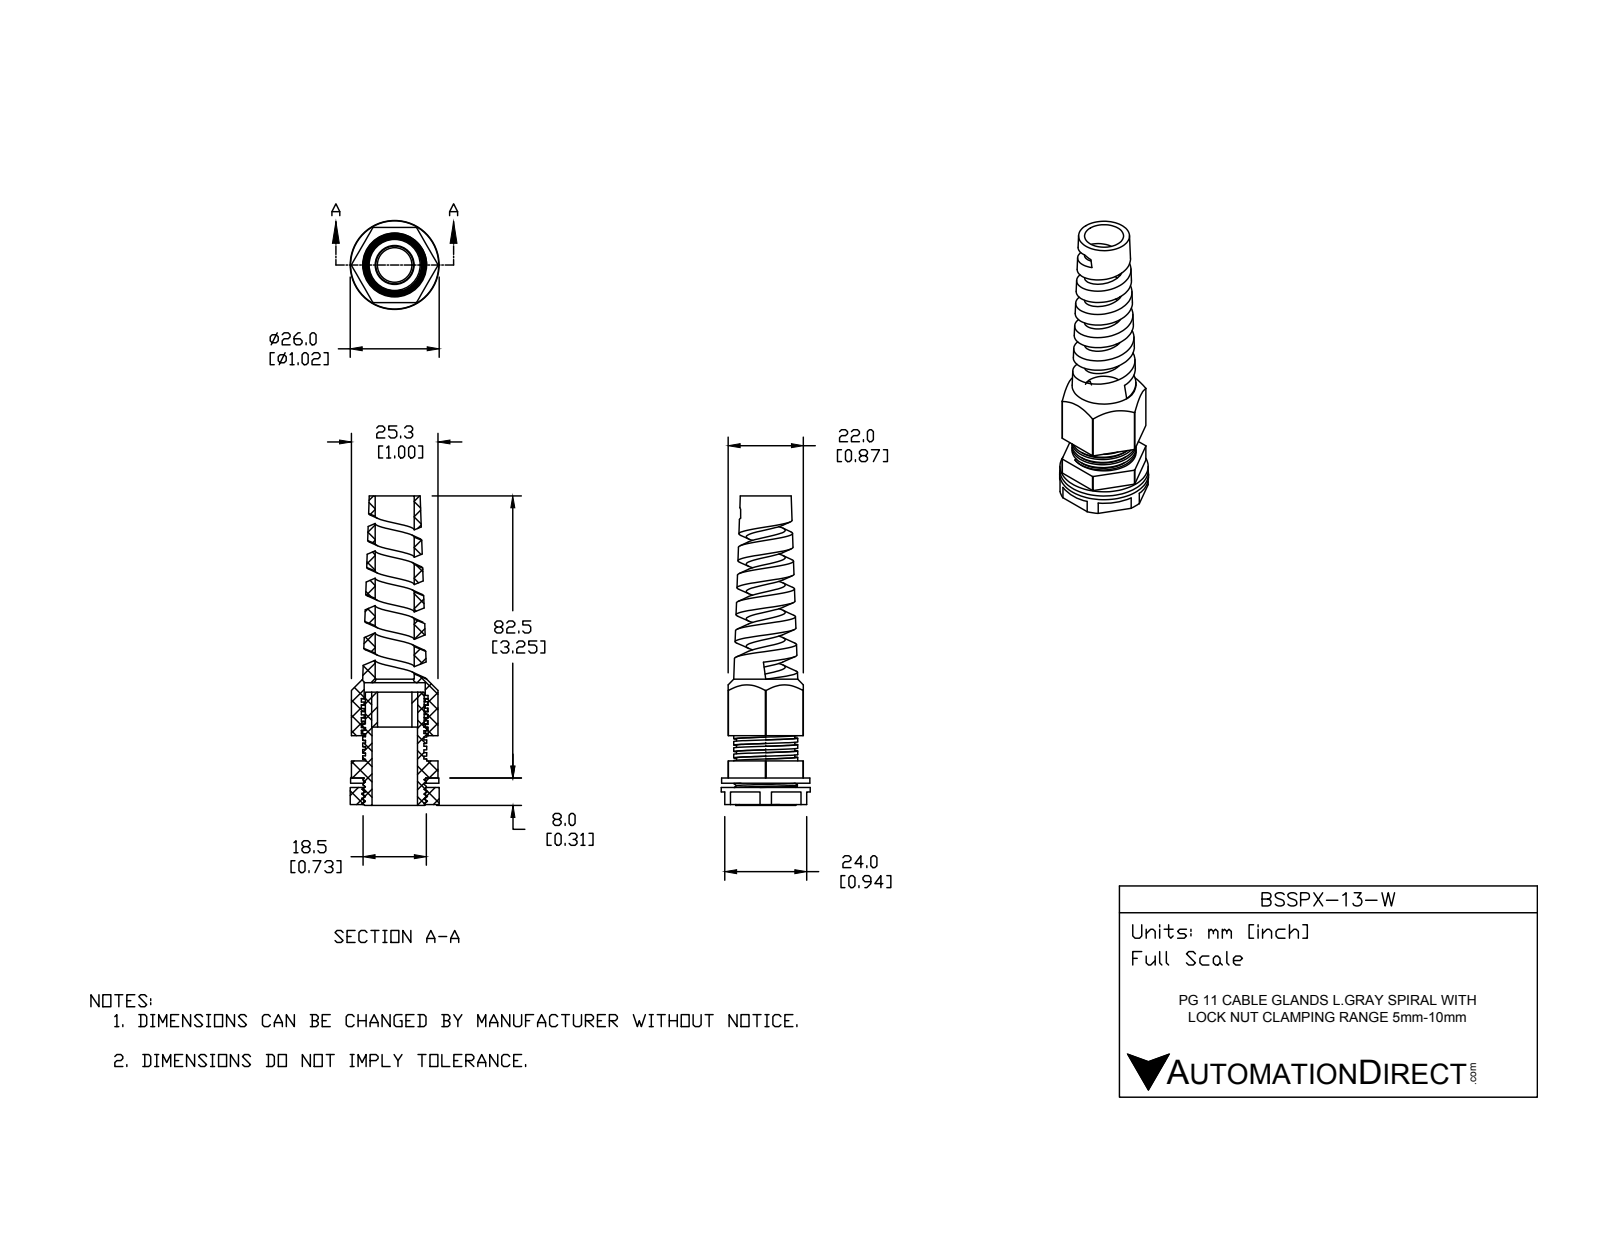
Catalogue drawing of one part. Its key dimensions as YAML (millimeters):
part_name: "BSSPX-13-W"
step_written_by: "SolidWorks 2015 (CONFIG_CONTROL_DESIGN)"
units: millimeters
bodies: {solids: 5, faces: 227, planar: 103, cylindrical: 90, other: 34}
overall_size: [90.5, 26, 26]
volume: 13012
surface_area: 15591
round_holes:
  - {diameter: 10.1, count: 1}
  - {diameter: 11.4, count: 1}
  - {diameter: 13.3, count: 1}
  - {diameter: 13.5, count: 1}
  - {diameter: 17.83, count: 1}
  - {diameter: 17.88, count: 1}
  - {diameter: 18.2, count: 1}
round_bosses_or_shafts:
  - {diameter: 26, count: 1}
  - {diameter: 25.8, count: 1}
  - {diameter: 18.7, count: 1}
  - {diameter: 18.5, count: 1}
  - {diameter: 17.2, count: 1}
partial_cylinders:
  - {radius: 12.65, count: 1}
face_to_face_distances: [22, 5, 7.75, 2.75, 6.5, 1.25, 1.5, 1, 6.25, 23]
